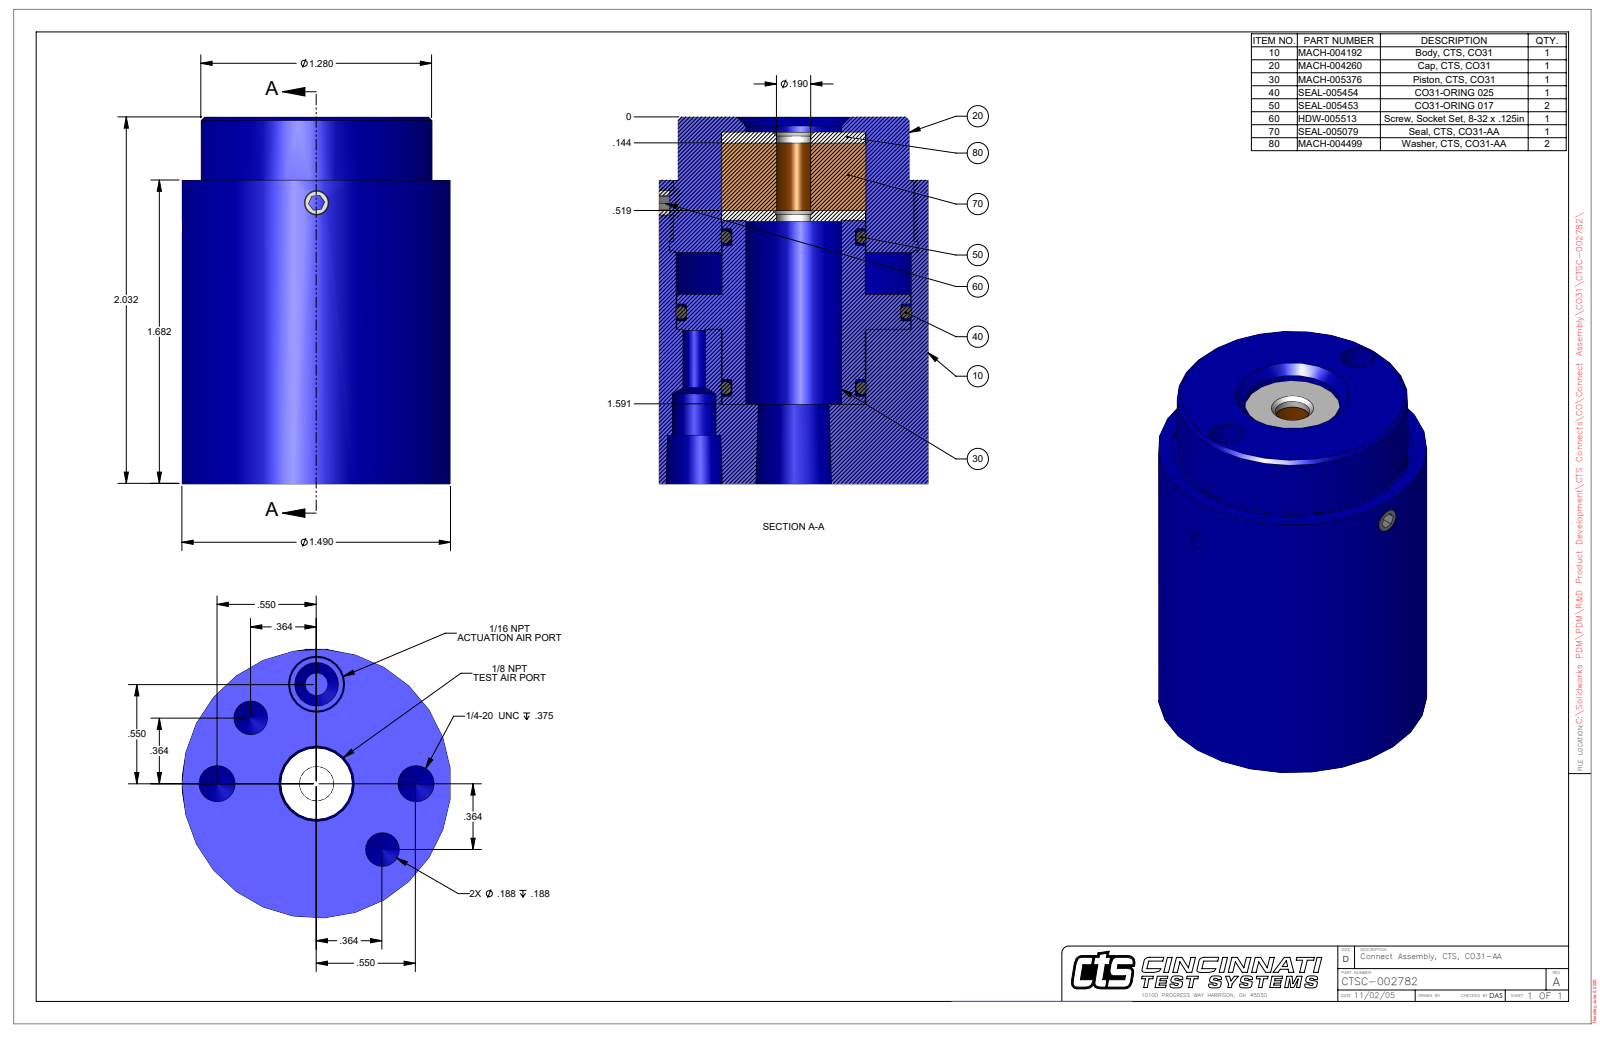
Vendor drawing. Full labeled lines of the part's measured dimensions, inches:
Part name (STEP PRODUCT): CTSC-002782
STEP written by: SolidWorks 2023 (AUTOMOTIVE_DESIGN)
Units: inches
Bodies: 1 solid, 111 faces (53 planar, 40 cylindrical, 18 other)
Overall size (bounding box): 2.032 × 1.49 × 1.49
Volume: 3.006 in³ · Surface area: 16.93 in²
Round holes (diameter × count): ⌀0.187 ×4, ⌀0.201 ×2, ⌀0.094 ×1, ⌀0.136 ×1, ⌀0.19 ×1, ⌀0.192 ×1, ⌀0.242 ×1, ⌀0.53 ×1, ⌀0.8 ×1, ⌀1.33 ×1
Round bosses / shafts (diameter × count): ⌀1.49 ×1, ⌀1.28 ×1, ⌀0.792 ×1
Partial cylindrical surfaces — rounded edges, fillets, slot ends (radius × count): R0.687 ×1, R0.735 ×1
Main face-to-face distances: 2.032, 1.682, 0.35, 1.454, 0.228, 0.578, 1.947, 0.493, 0.265, 0.085
Hole centre spacings: 0.515, 0.409, 0.55, 0.984, 0.035, 0.394, 0.754, 0.778
